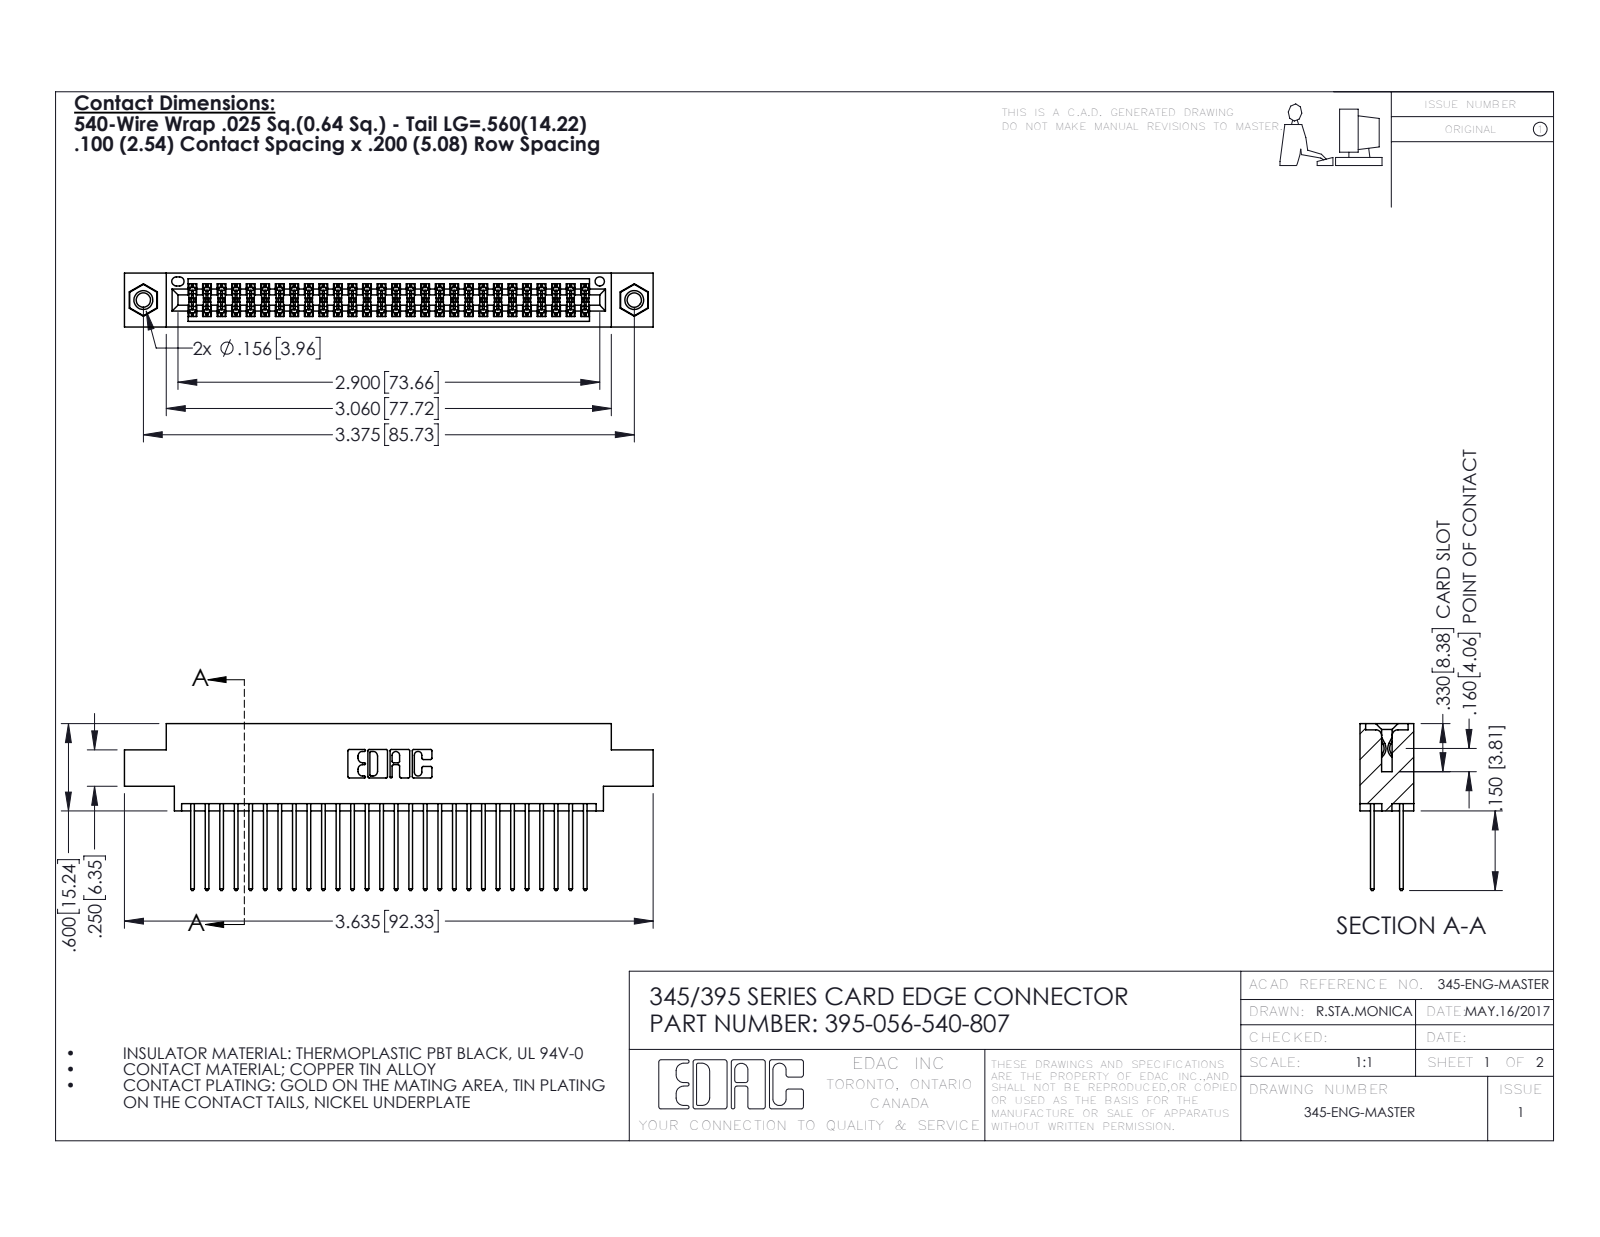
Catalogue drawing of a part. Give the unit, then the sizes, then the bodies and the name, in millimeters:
Units: millimetres
Overall size (bounding box): 92.3 × 29.1 × 9.4
Round holes (diameter × count): ⌀2.5 ×2, ⌀3.2 ×2, ⌀4 ×2, ⌀1.6 ×1
Round bosses / shafts (diameter × count): ⌀3.9 ×2
Partial cylindrical surfaces — rounded edges, fillets, slot ends (radius × count): R0.2 ×84, R0.3 ×56, R0.3 ×22, R0.2 ×6, R0.8 ×6, R0.7 ×3, R0.4 ×2, R0.5 ×2
Main face-to-face distances: 1.8, 7.6, 5.1, 2.5, 6.9, 0.6, 9.4, 5.7, 4.4, 3.8
Hole centre spacings: 6.9, 79.8, 85.7
Volume: 8 930 mm³ · Surface area: 14 080 mm²
Bodies: 59 solids, 2990 faces (1964 planar, 1010 cylindrical, 16 other)
Part name (STEP PRODUCT): 345-250-001_345-250-005-103; 395-056-540-807; 345-292-001_345-293-140; 345 Part_0.170 Offset - 0.156 Dia-TI
STEP written by: SolidWorks 2016 (CONFIG_CONTROL_DESIGN)
